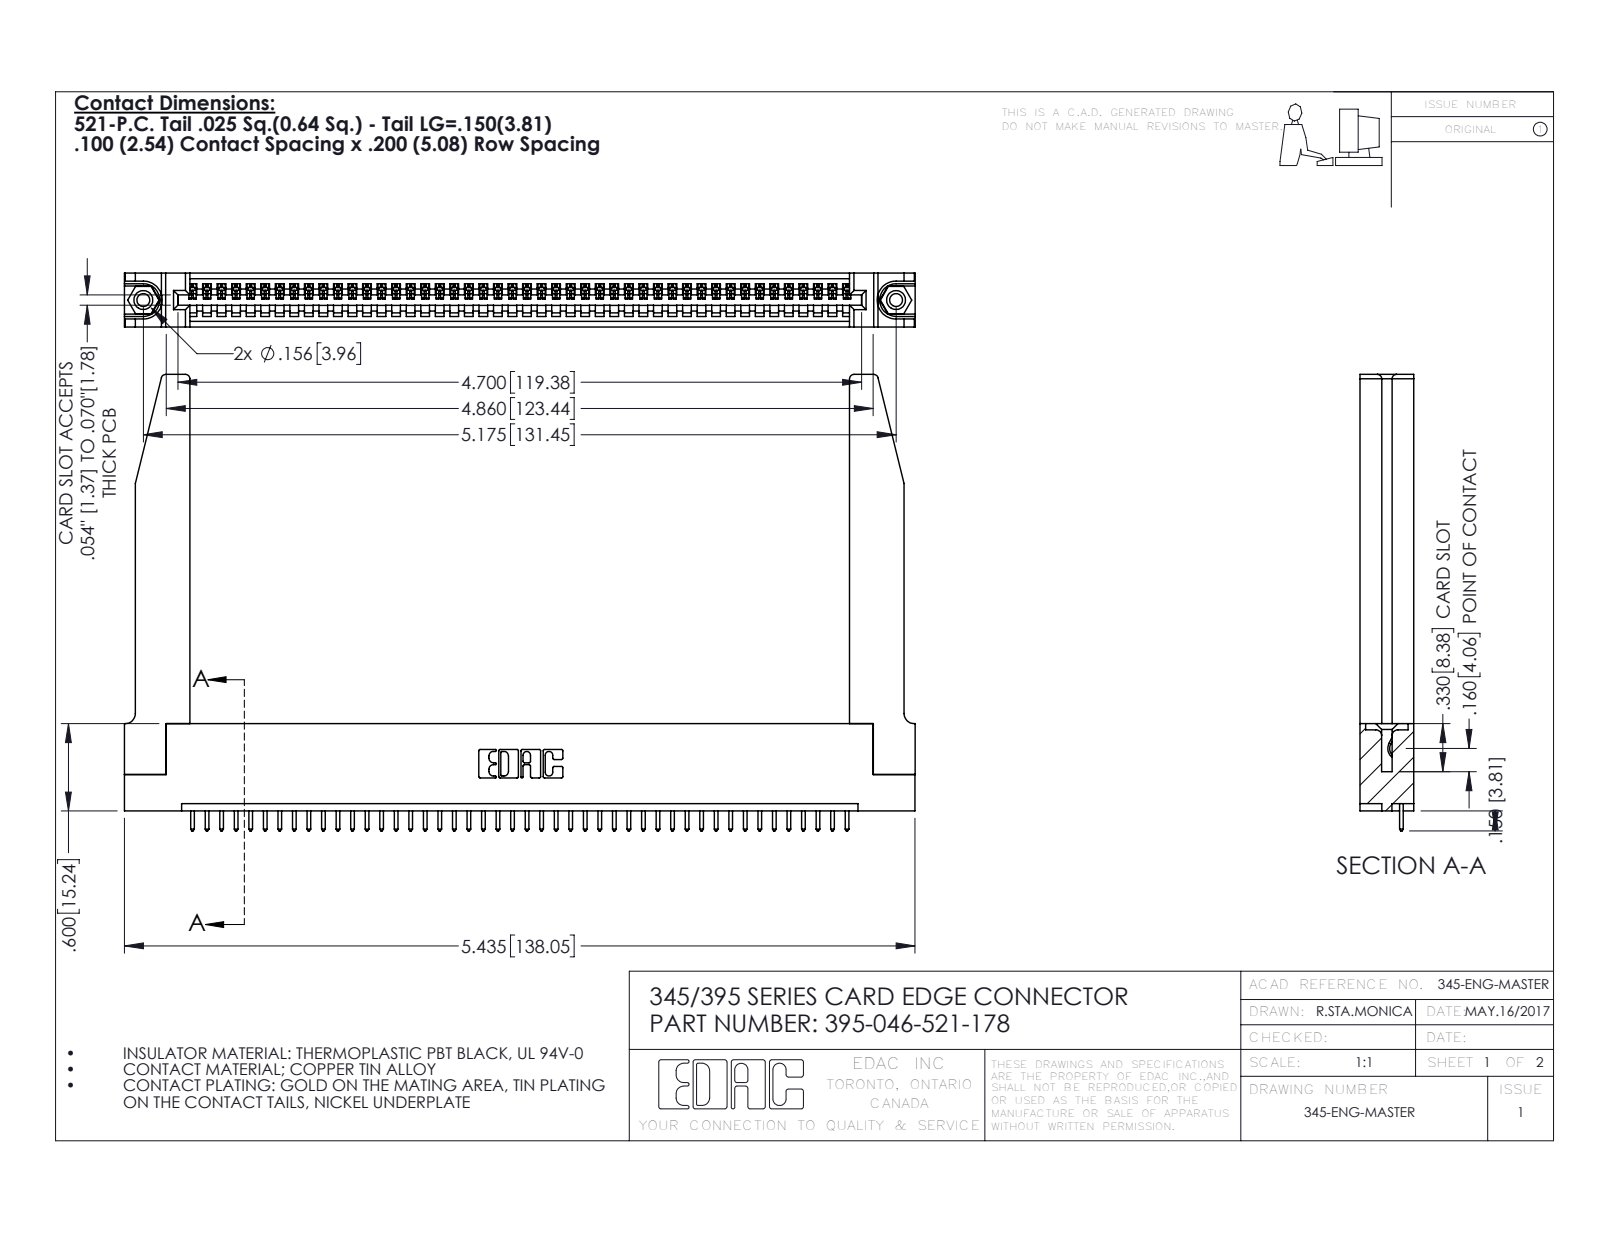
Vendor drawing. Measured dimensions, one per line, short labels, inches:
name: 395-046-521-178; 345 Part_Flush Mounting Lugs - 0.156 Dia-TH; 345-220-078_345-220-078; 345-250-001_345-250-001-102 (+1 more)
written by: SolidWorks 2016 (CONFIG_CONTROL_DESIGN)
unit: in
bodies: 51 solids, 3028 faces (2062 planar, 914 cylindrical, 52 other)
size: 5.436 × 3.137 × 0.37
volume: 1.268 in³; area: 36.71 in²
holes: 2× ⌀0.089, 2× ⌀0.125, 2× ⌀0.156, 1× ⌀0.064
bosses: 2× ⌀0.155
rounds: 92× R0.006, 92× R0.01, 22× R0.01, 8× R0.03, 6× R0.007, 6× R0.031, 3× R0.026, 2× R0.031
face distances: 0.37, 0.072, 0.298, 0.2, 0.098, 0.272, 0.025, 0.225, 0.148, 0.15
hole spacings: 0.27, 4.939, 5.175
